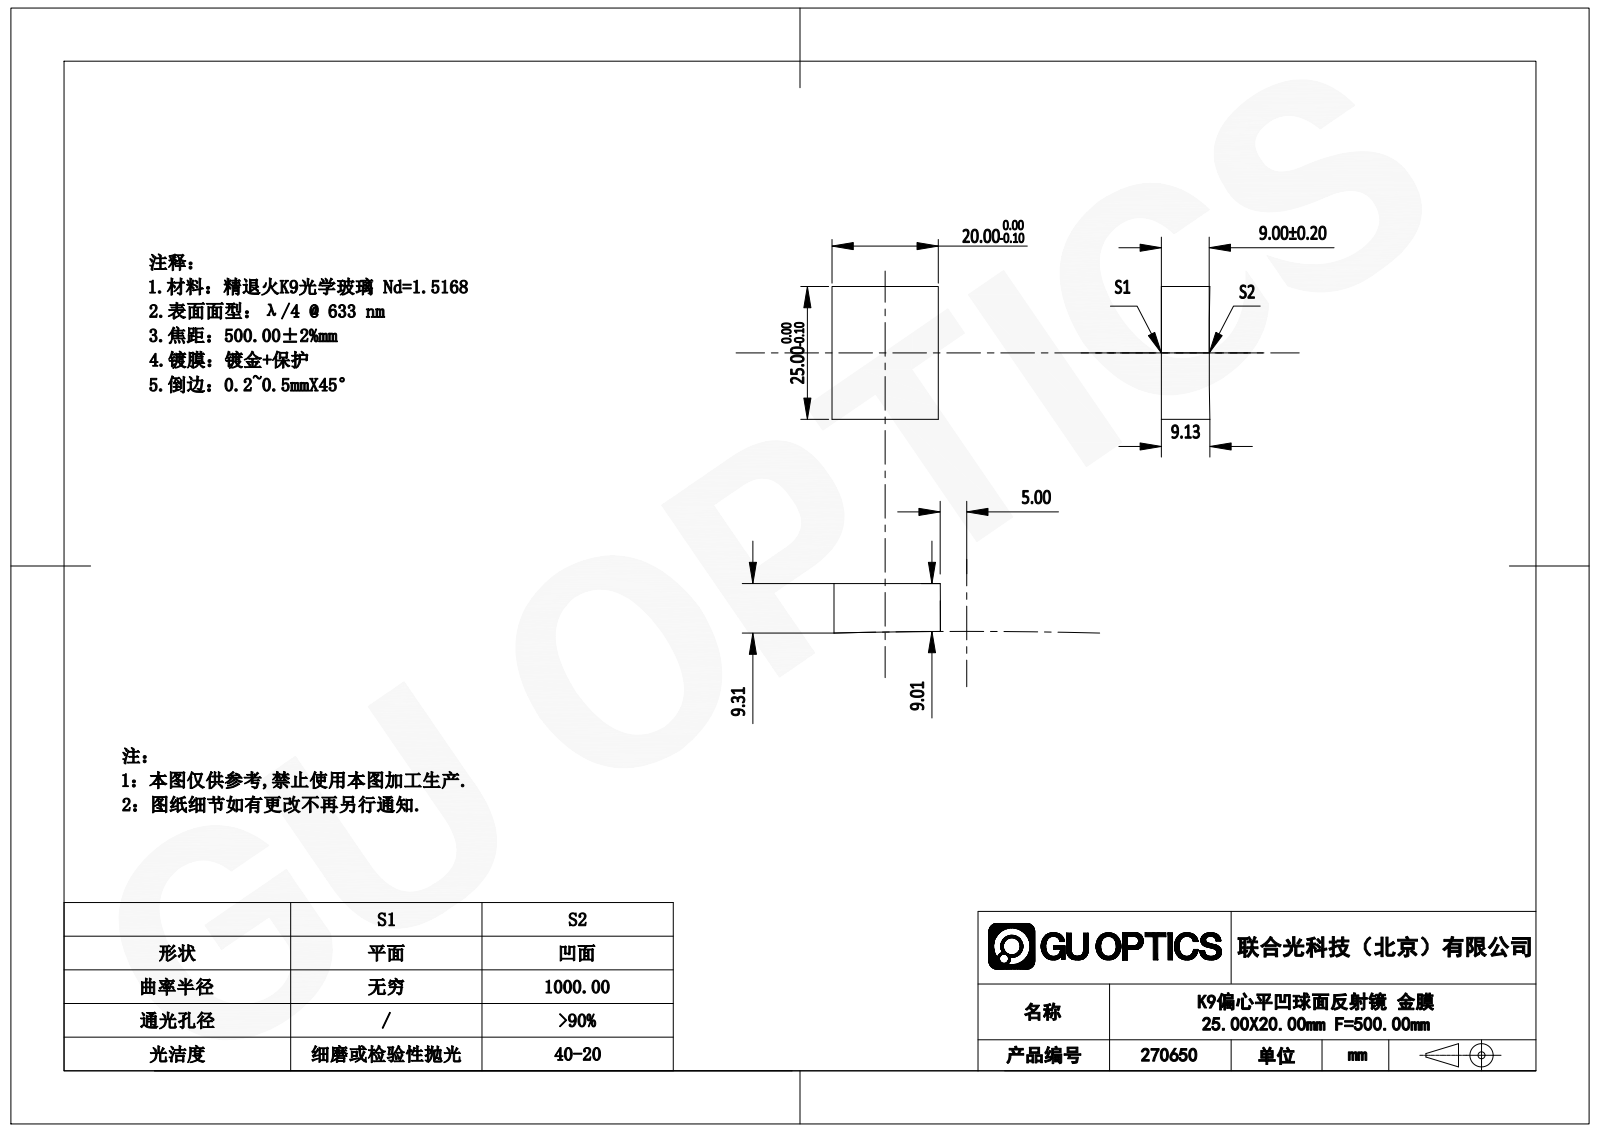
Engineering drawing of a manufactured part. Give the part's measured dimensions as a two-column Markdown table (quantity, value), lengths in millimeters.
| quantity | value |
| --- | --- |
| part name | 270650 |
| STEP written by | SolidWorks 2020 (CONFIG_CONTROL_DESIGN) |
| units | millimeters |
| bodies | 1 solid, 7 faces (5 planar, 0 cylindrical, 2 other) |
| overall size | 25 × 20 × 9.39 |
| volume | 4 578 mm³ |
| surface area | 1 828 mm² |
| main face-to-face distances | 20, 25 |
